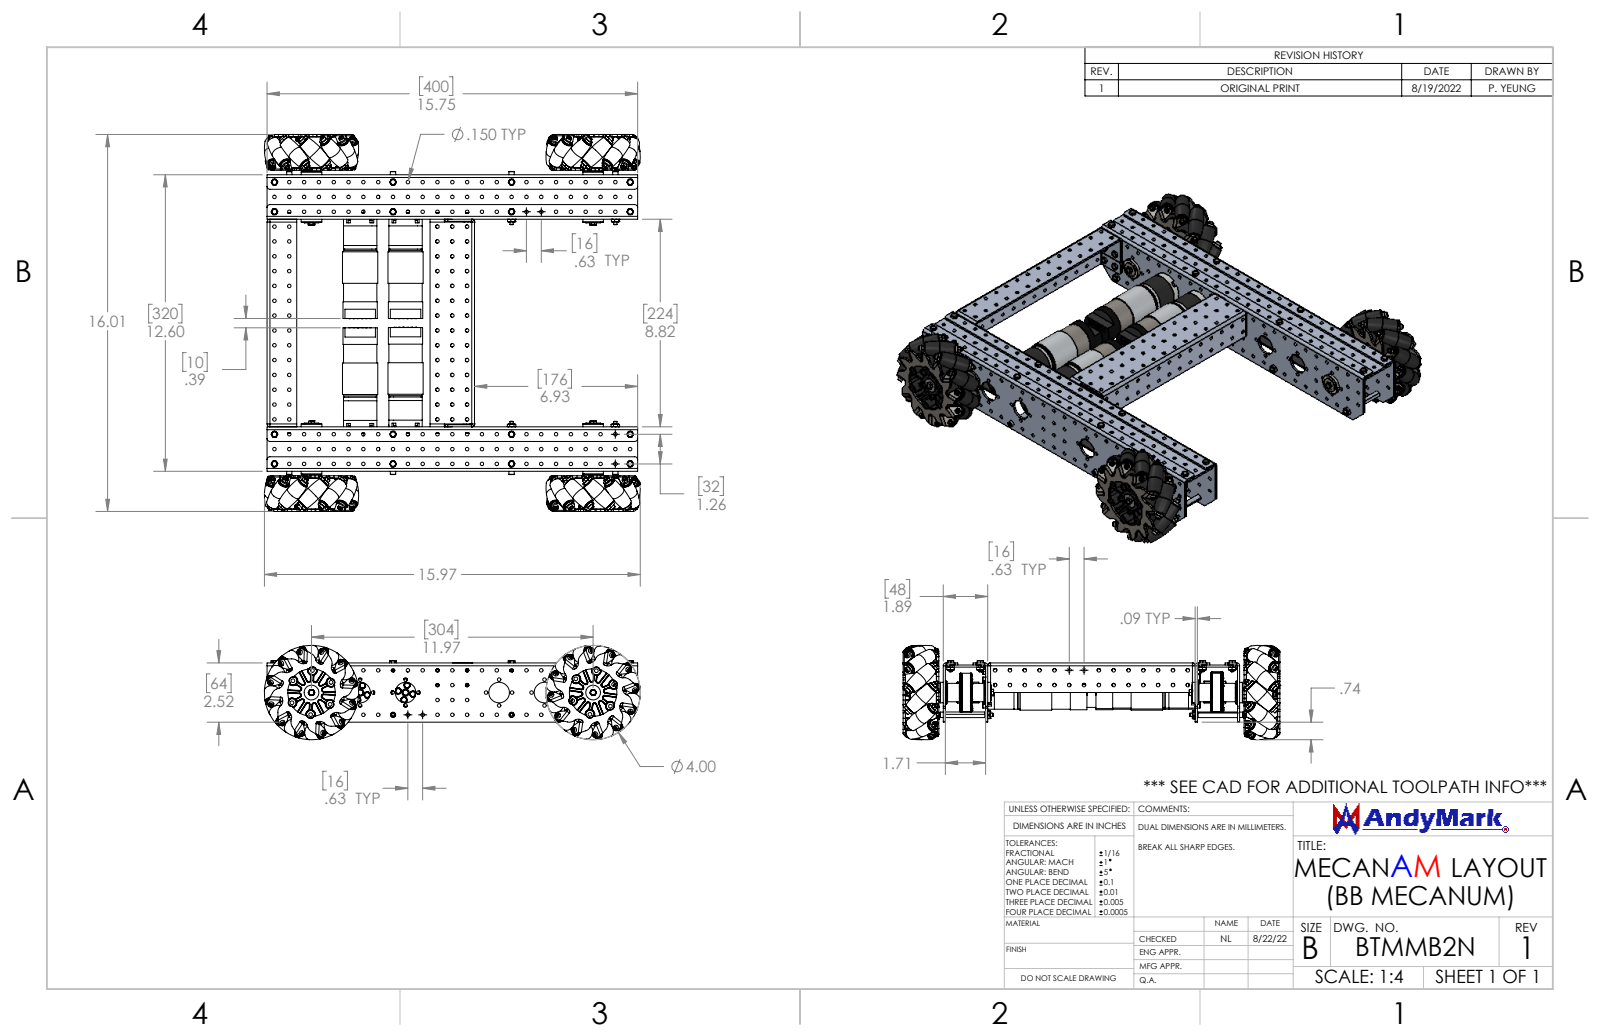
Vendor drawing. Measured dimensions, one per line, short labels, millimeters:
name: 4in Mecanum Left 0375H Bore; SHCS M3 x 16mm; 4IN BB Mecanum Roller Skin; 6-32 x 0375 HHCS_93075A146 (+8 more)
written by: SolidWorks 2022 (AUTOMOTIVE_DESIGN)
unit: mm
bodies: 2156 solids, 50032 faces (8544 planar, 18212 cylindrical, 23276 other)
size: 406.7 × 405.7 × 101.7
volume: 1 644 000 mm³; area: 1 275 000 mm²
holes: 352× ⌀3.8, 120× ⌀2.9, 95× ⌀3.4, 94× ⌀4.7, 94× ⌀5.9, 94× ⌀7.7, 94× ⌀11.1, 59× ⌀3.2, 50× ⌀9.5, 48× ⌀3.1, 48× ⌀7, 30× ⌀2.5
bosses: 94× ⌀9.5, 71× ⌀5.5, 71× ⌀3, 42× ⌀3.5, 26× ⌀3.8, 11× ⌀2.4, 5× ⌀42, 4× ⌀5.9
rounds: 904× R0.3, 384× R0.3, 384× R0.4, 384× R0.4, 384× R1.4, 384× R1.8, 384× R2.3, 384× R2.8
face distances: 2.3, 45.7, 272, 48, 226.3, 43.4, 269.7, 274.3, 317.7, 2.3
hole spacings: 16, 32, 48, 80, 35.8, 50.6, 64, 96
